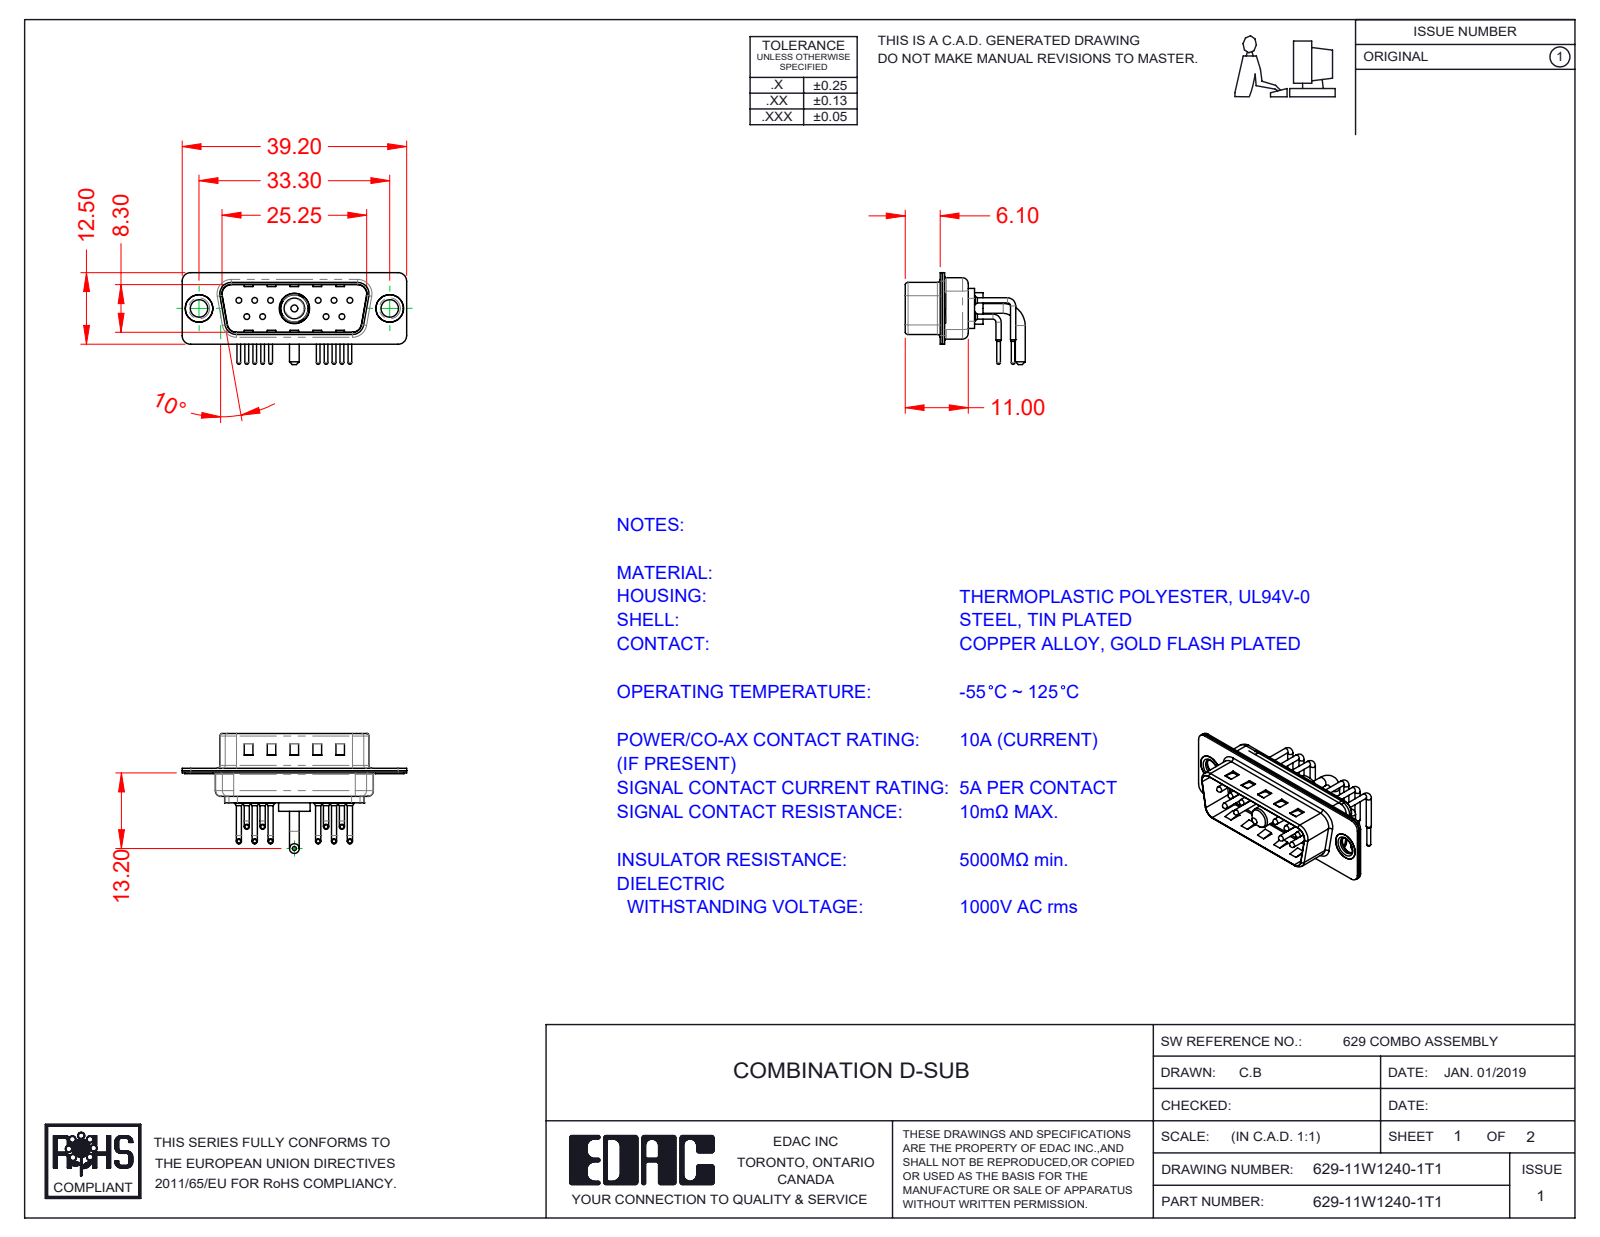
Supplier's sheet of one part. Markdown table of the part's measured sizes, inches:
| quantity | value |
| --- | --- |
| part name | 629Combo Shell Rear_15 Contacts; 629Combo Contact Row 1; 629Combo Contact Row 2; 629-11W1240-1T1 (+4 more) |
| STEP written by | SolidWorks 2020 (CONFIG_CONTROL_DESIGN) |
| units | inches |
| bodies | 17 solids, 1470 faces (798 planar, 502 cylindrical, 170 other) |
| overall size | 1.543 × 0.825 × 0.632 |
| volume | 0.118 in³ |
| surface area | 7.807 in² |
| round holes (diameter × count) | 0.03 × 10, 0.063 × 10, 0.079 × 10, 0.12 × 2, 0.157 × 2, 0.189 × 2, 0.191 × 1, 0.209 × 1 |
| round bosses / shafts (diameter × count) | 0.035 × 20, 0.059 × 10, 0.039 × 10, 0.026 × 10, 0.197 × 2, 0.193 × 2, 0.14 × 2, 0.067 × 2 |
| partial cylindrical surfaces (radius × count) | 0.059 × 16, 0.079 × 12, 0.04 × 10, 0.02 × 8, 0.063 × 8, 0.039 × 7, 0.01 × 4, 0.024 × 4 |
| main face-to-face distances | 0.016, 0.031, 0.374, 0.358, 0.343, 0.39, 0.22, 0.03, 0.047, 0.014 |
| hole center spacings | 0.124, 0.109, 0.545, 0.436, 0.654, 0.198, 0.198, 0.218 |
